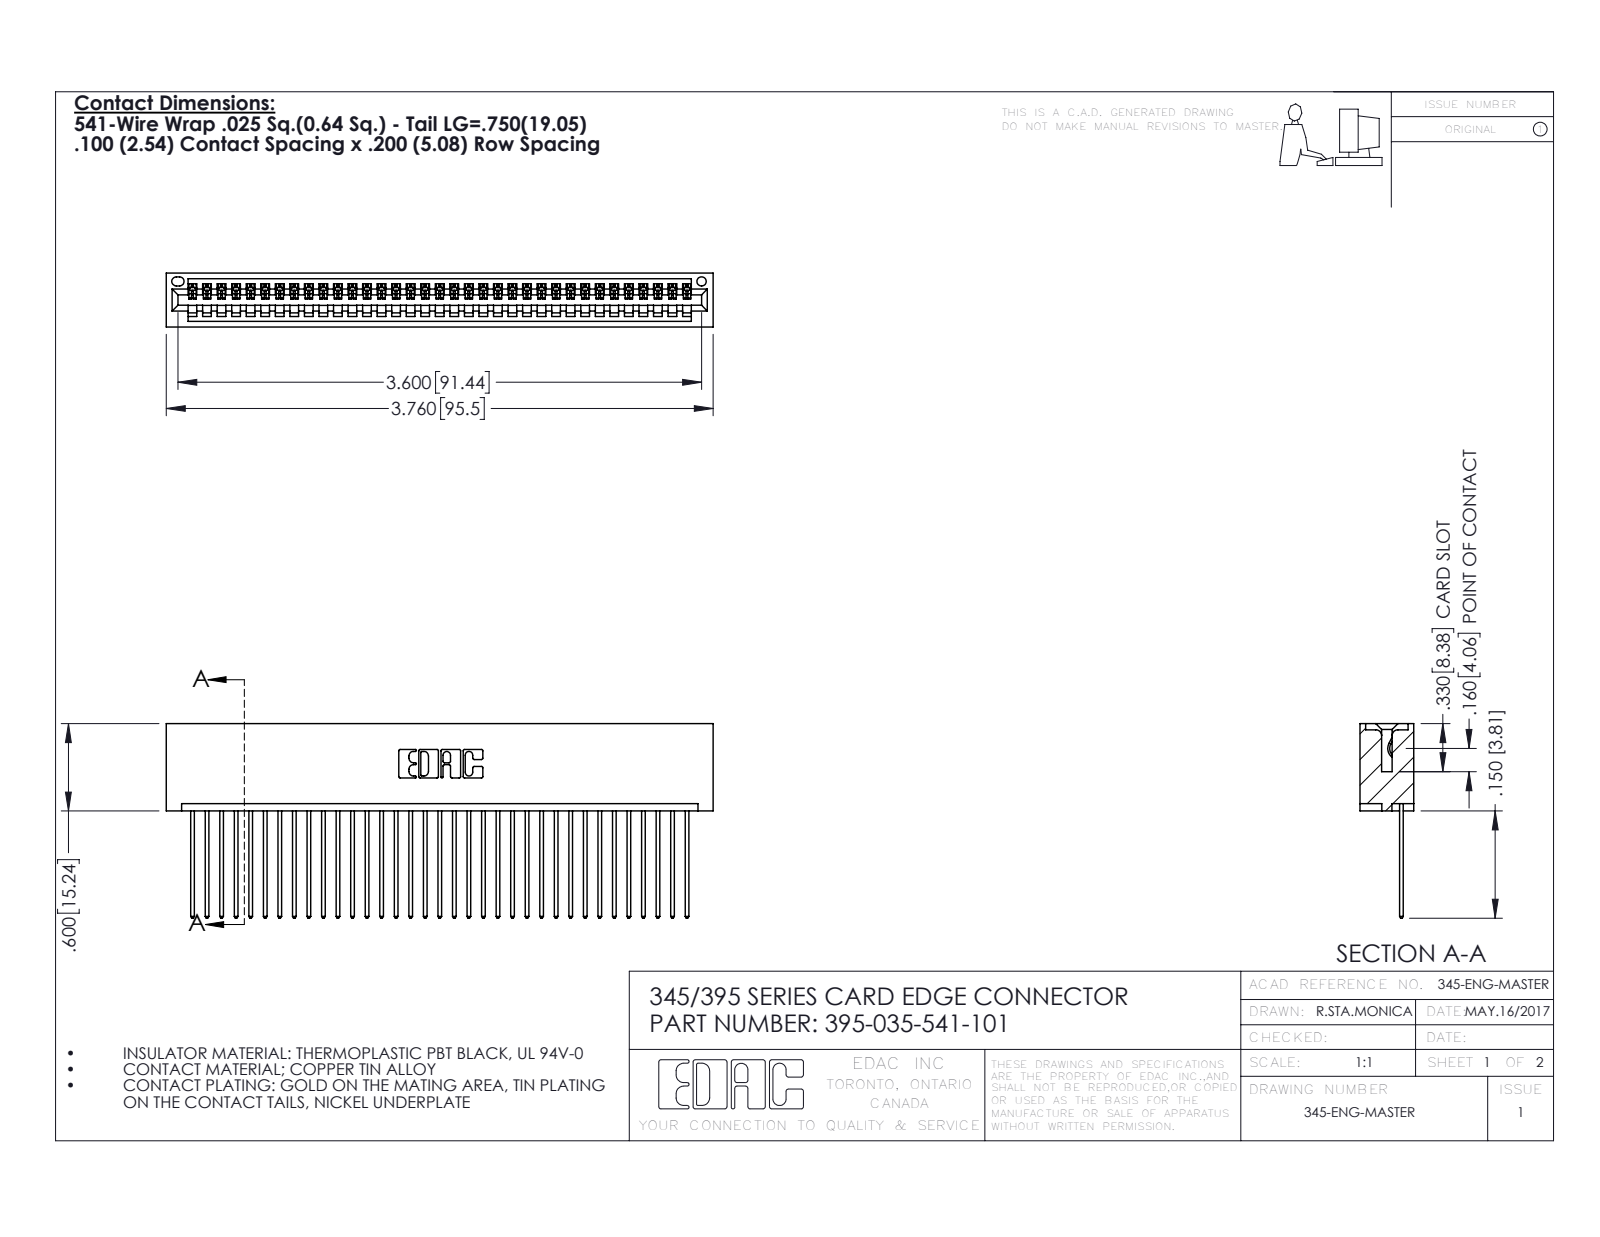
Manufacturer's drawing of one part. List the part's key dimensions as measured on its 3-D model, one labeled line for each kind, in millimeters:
Part name (STEP PRODUCT): 345-292-001_345-293-141; 345 Part_No Mounting Lugs; 395-035-541-101
STEP written by: SolidWorks 2016 (CONFIG_CONTROL_DESIGN)
Units: millimetres
Bodies: 36 solids, 2148 faces (1476 planar, 672 cylindrical, 0 other)
Overall size (bounding box): 95.5 × 34 × 9.4
Volume: 9 720 mm³ · Surface area: 13 680 mm²
Round holes (diameter × count): ⌀1.6 ×1
Partial cylindrical surfaces — rounded edges, fillets, slot ends (radius × count): R0.2 ×70, R0.3 ×70, R0.3 ×22, R0.2 ×6, R0.8 ×6, R0.7 ×3, R0.8 ×2, R1 ×2
Main face-to-face distances: 1.8, 7.6, 2.5, 6.9, 0.6, 5.1, 9.4, 5.7, 3.8, 1.8
